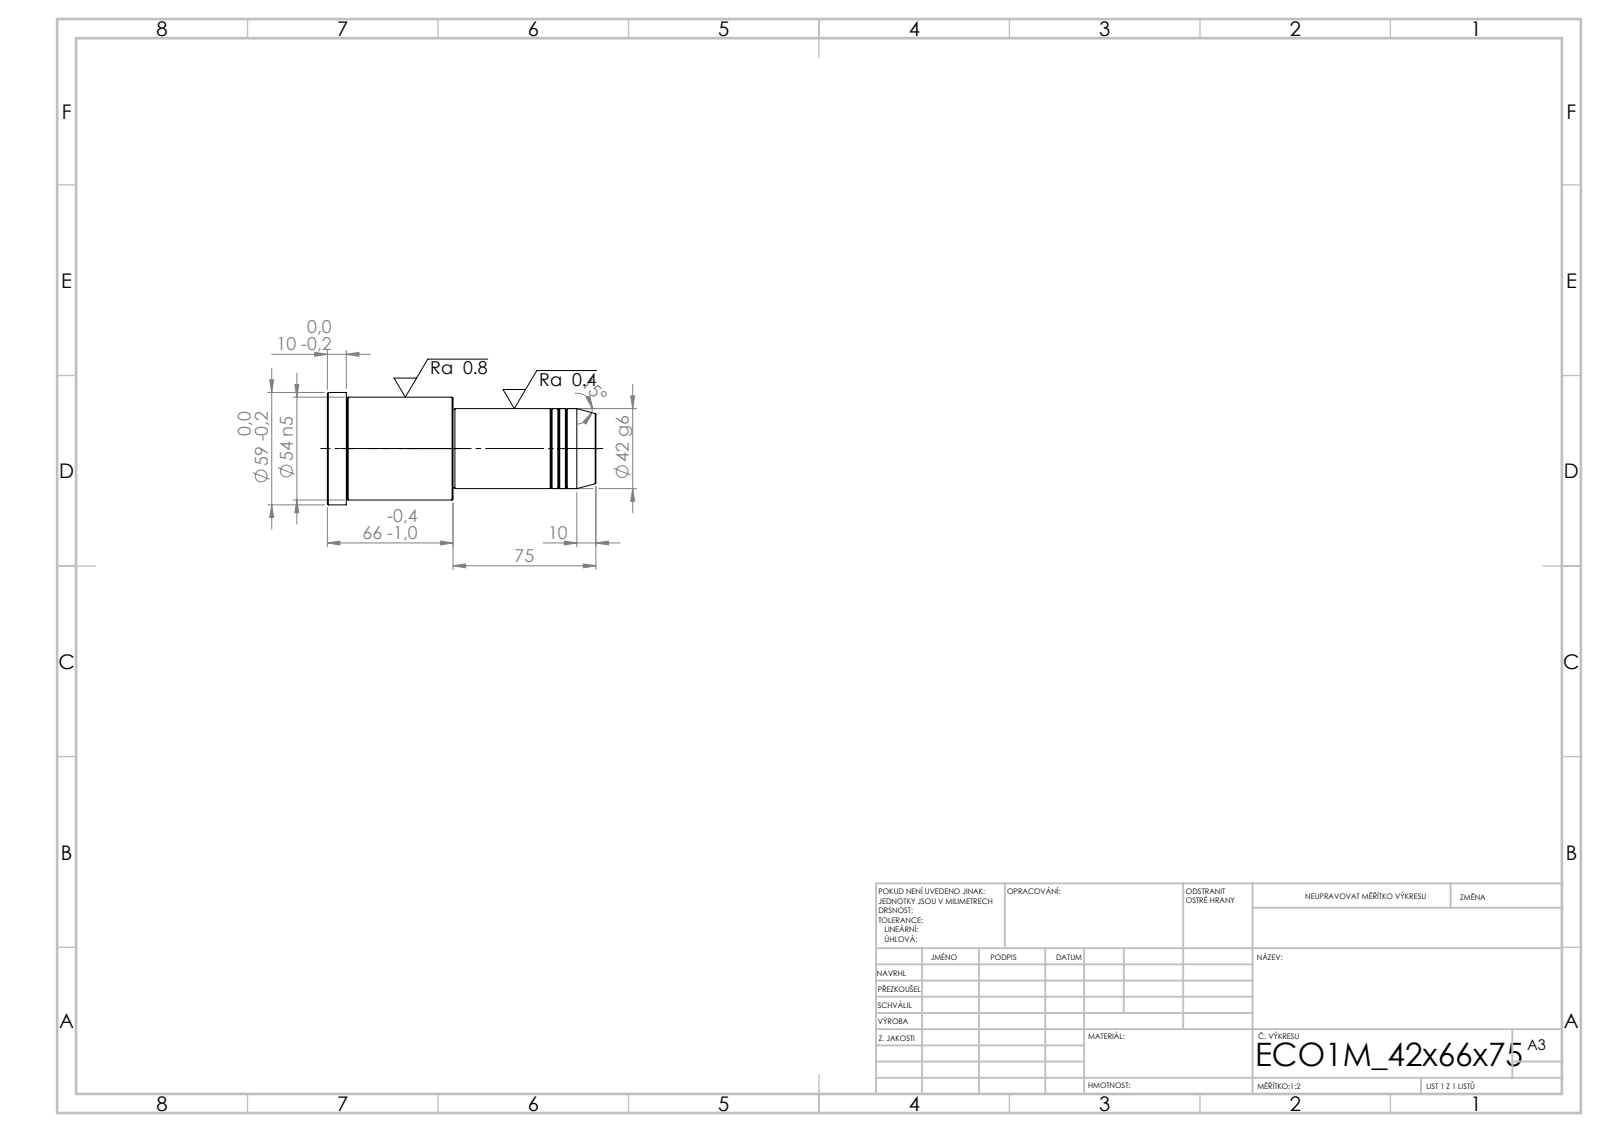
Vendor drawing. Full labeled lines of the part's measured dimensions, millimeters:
STEP written by: SolidWorks 2019 (CONFIG_CONTROL_DESIGN)
Units: millimetres
Bodies: 1 solid, 43 faces (5 planar, 14 cylindrical, 24 other)
Overall size (bounding box): 141 × 59 × 59
Volume: 257 475 mm³ · Surface area: 26 666 mm²
Round bosses / shafts (diameter × count): ⌀59 ×1, ⌀54 ×1, ⌀42 ×1, ⌀41 ×1
Main face-to-face distances: 141, 75, 66, 131, 56, 10, 74, 1, 57, 67
